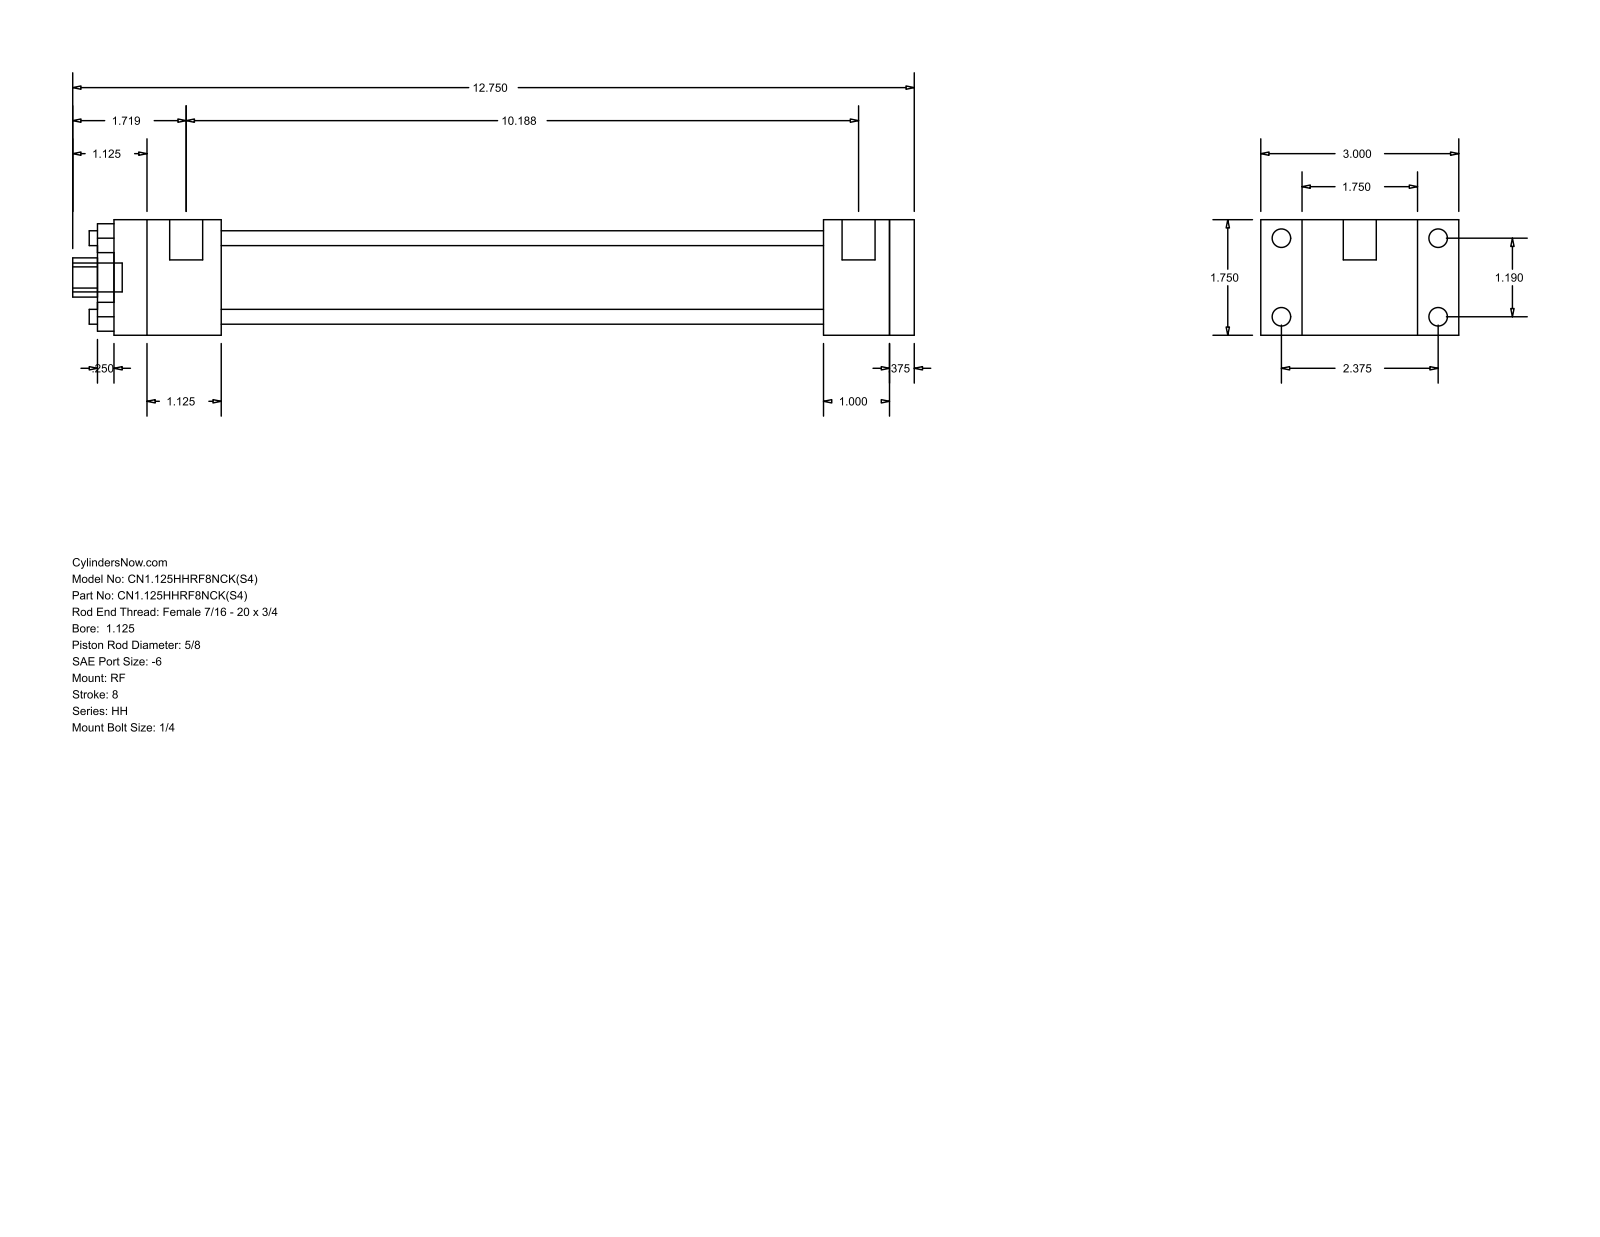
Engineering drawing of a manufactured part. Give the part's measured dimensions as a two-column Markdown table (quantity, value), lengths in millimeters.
| quantity | value |
| --- | --- |
| part name | HH_RF__0112_0.625 |
| STEP written by | GSSL Pune (CONFIG_CONTROL_DESIGN) |
| units | millimeters |
| bodies | 0 solids, 92 faces (64 planar, 28 cylindrical, 0 other) |
| overall size | 323.85 × 76.2 × 44.45 |
| round holes (diameter × count) | 5.71 × 4, 15.88 × 1, 28.57 × 1, 34.92 × 1 |
| round bosses / shafts (diameter × count) | 7.14 × 4, 5.56 × 4, 12.7 × 2, 11.11 × 1 |
| partial cylindrical surfaces (radius × count) | 7.54 × 1 |
| main face-to-face distances | 44.46, 9.53, 307.97, 15.87, 257.17, 266.7, 231.78, 25.39, 34.92, 41.27 |
| hole center spacings | 21.37, 30.22, 42.74 |
